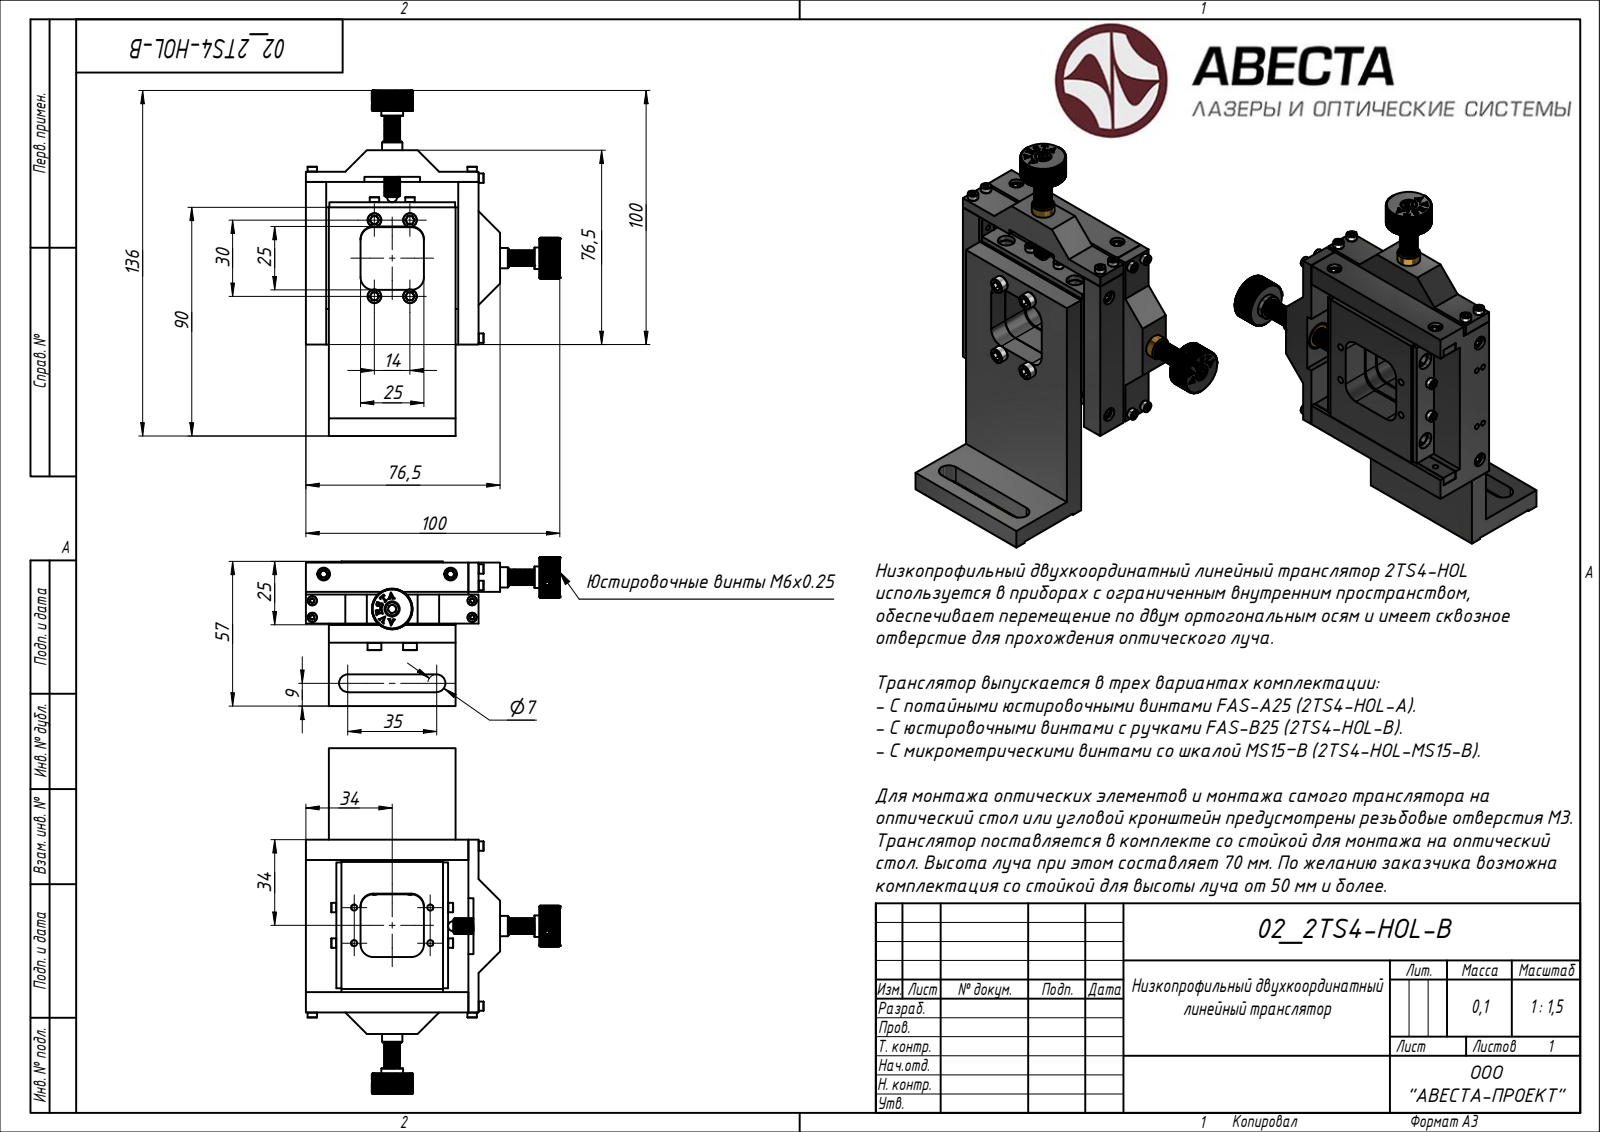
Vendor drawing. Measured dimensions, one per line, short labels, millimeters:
written by: Rhino 7.34 (AUTOMOTIVE_DESIGN)
unit: mm
bodies: 16 solids, 2957 faces (1752 planar, 822 cylindrical, 383 other)
size: 136 × 100 × 58.75
volume: 109 910 mm³; area: 62 636 mm²
holes: 9× ⌀2.01, 6× ⌀2.46, 4× ⌀1.57, 4× ⌀5, 4× ⌀6, 3× ⌀1.57, 2× ⌀2.46, 2× ⌀3, 2× ⌀3.1, 2× ⌀10, 1× ⌀2.01
bosses: 14× ⌀3, 12× ⌀3.7, 5× ⌀2, 4× ⌀5.4, 4× ⌀4.5, 2× ⌀9, 2× ⌀8.5, 2× ⌀8
rounds: 8× R3, 8× R5, 6× R0.78, 4× R0.78, 4× R1.1, 4× R1.23, 4× R1.23, 3× R1.01
face distances: 15, 9.5, 10, 9, 7.5, 5, 0.5, 7, 2, 8
hole spacings: 31.67, 15.07, 17.15, 24.91, 33.11, 35.03, 46.18, 6.67
